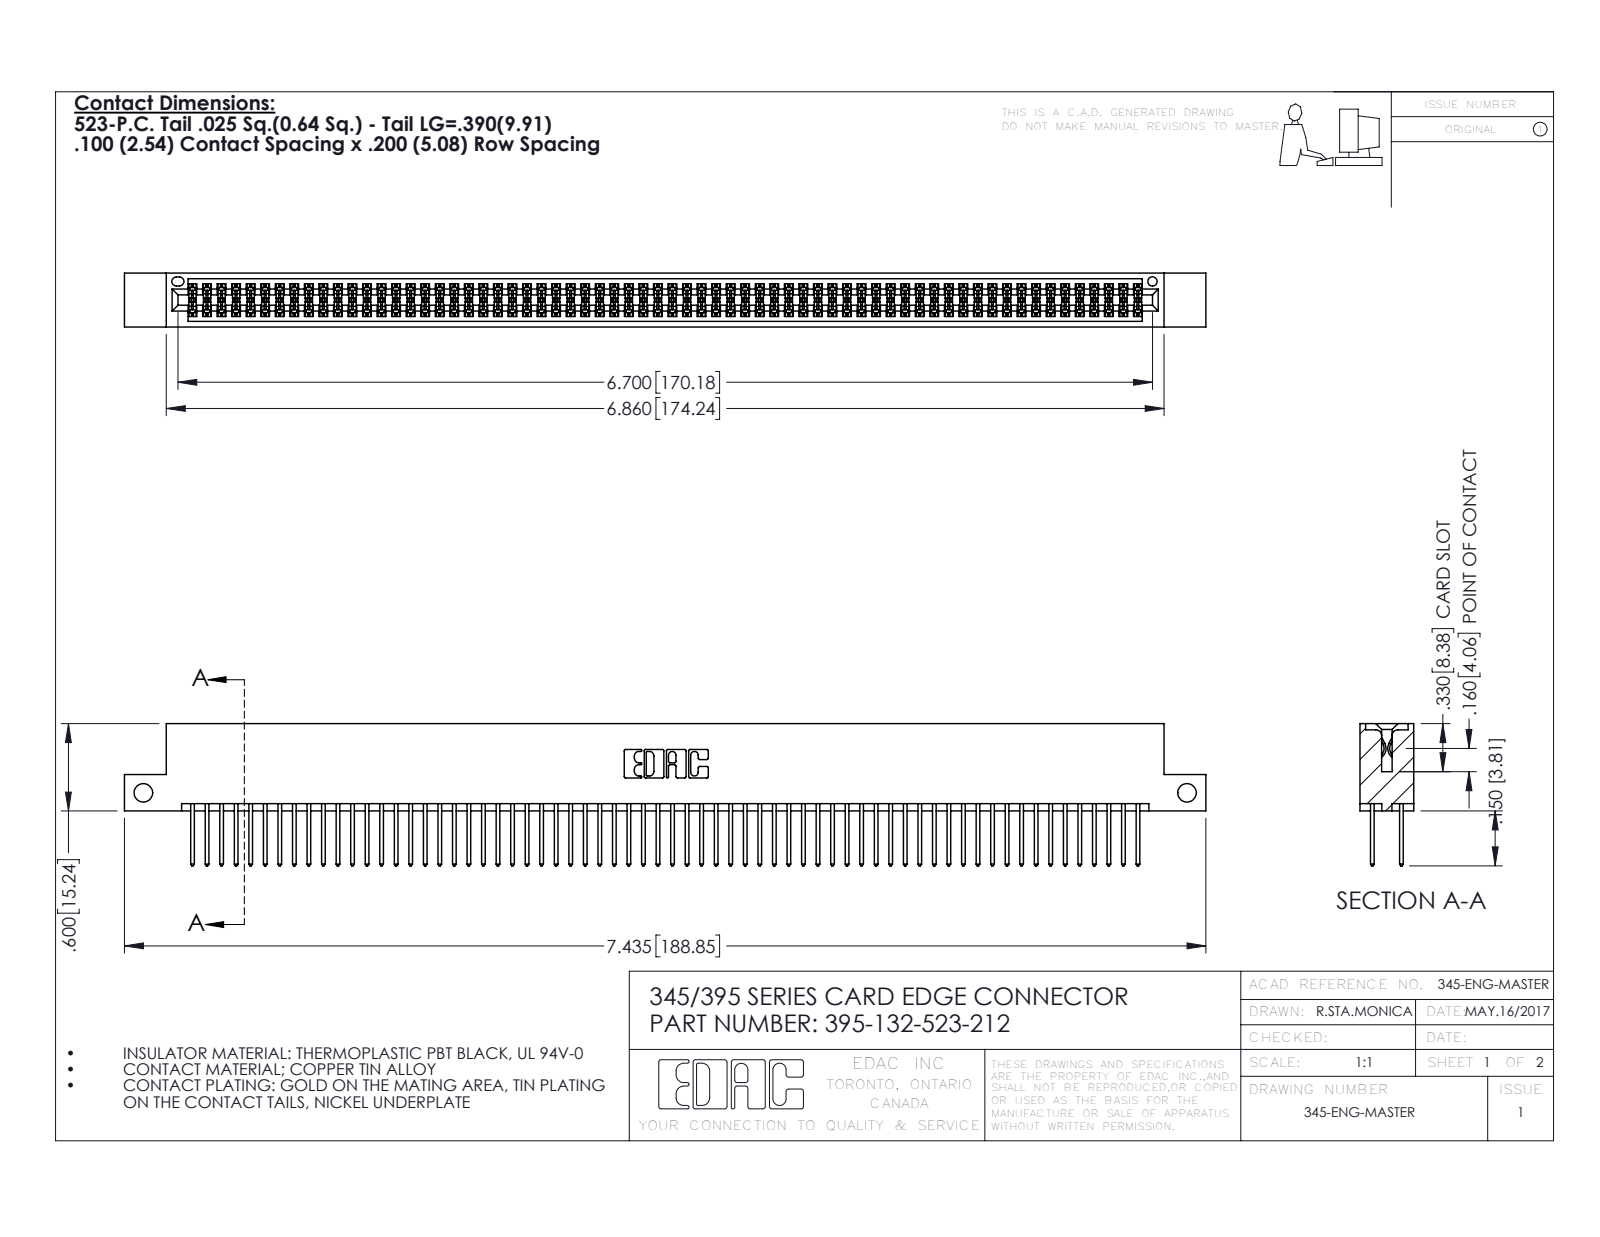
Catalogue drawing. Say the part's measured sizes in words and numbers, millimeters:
The part is named "345-292-001_345-293-123; 345 Part_Flush Mounting Lugs - Side Mount; 395-132-523-212". Its 3-D file was written by "SolidWorks 2016 (CONFIG_CONTROL_DESIGN)". It is 133 solids with 6726 faces: 4436 planar, 2290 cylindrical and 0 other. Overall it measures 188.8 by 24.8 by 9.4 millimeters. Its volume is 18 750 cubic millimeters and its surface area 29 260 square millimeters. Round holes: 2 of diameter 3.3, 1 of diameter 1.6. Partial cylindrical surfaces (rounded edges, fillets, slot ends): 198 of radius 0.2, 132 of radius 0.3, 22 of radius 0.3, 6 of radius 0.2, 6 of radius 0.8, 3 of radius 0.7, 2 of radius 0.4, 2 of radius 0.5. The main face-to-face distances are 7.6, 1.8, 5.1, 2.5, 6.9, 0.6, 9.4, 5.7, 4.4, 3.8. The hole center spacings are 182.2.
